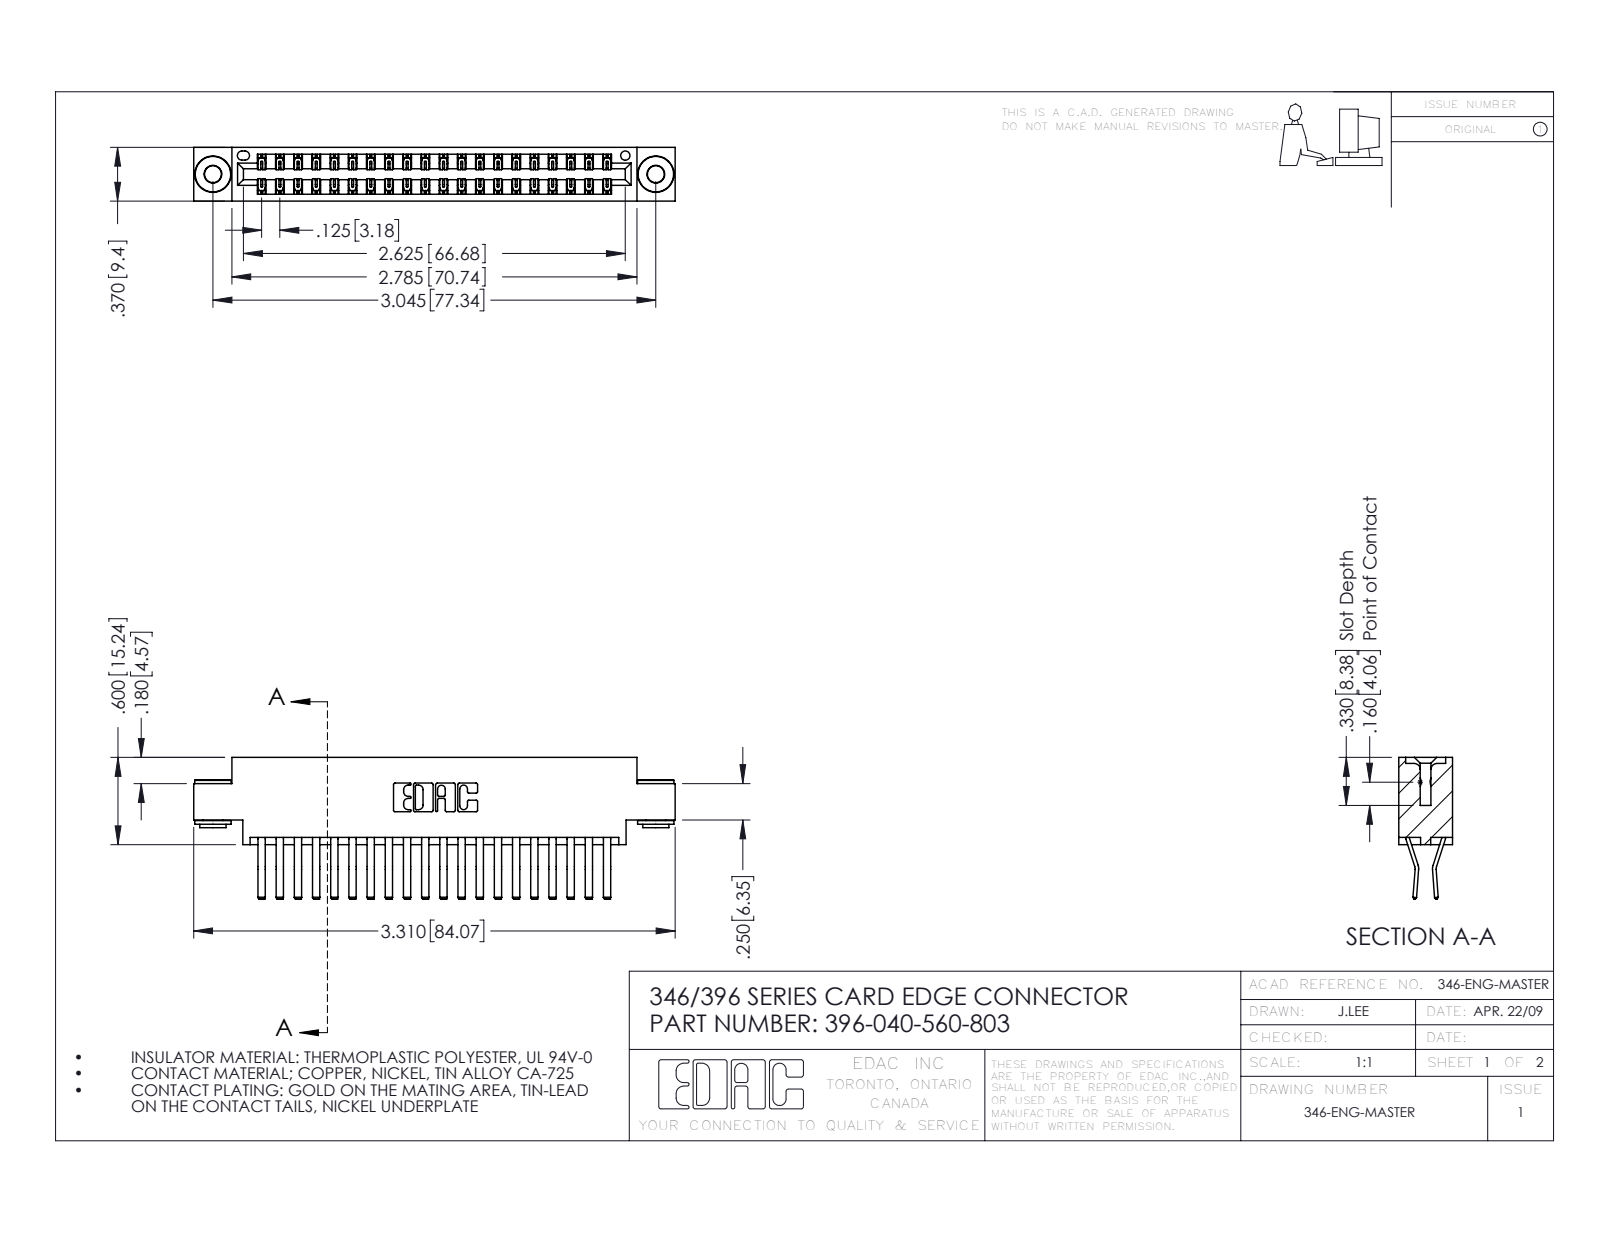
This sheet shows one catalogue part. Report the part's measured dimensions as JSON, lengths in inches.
{"part_name": "346 Part_0.170 Offset - 0.156 Dia-TH; 345-292-001_560 Tail; 396-040-560-803; 345-250-002_345-250-002-102", "step_written_by": "SolidWorks 2016 (CONFIG_CONTROL_DESIGN)", "units": "inches", "bodies": {"solids": 43, "faces": 2324, "planar": 1490, "cylindrical": 826, "other": 8}, "overall_size": [3.31, 0.975, 0.37], "volume_in3": 0.498, "surface_area_in2": 18.53, "round_holes": [[0.116, 2], [0.156, 2], [0.064, 1]], "round_bosses_or_shafts": [[0.25, 2], [0.18, 2], [0.136, 2]], "partial_cylinders_radius": [[0.006, 60], [0.01, 22], [0.007, 6], [0.031, 6], [0.026, 3], [0.01, 2], [0.014, 2], [0.022, 2]], "face_to_face_distances": [0.048, 0.322, 0.37, 0.25, 0.025, 0.275, 0.072, 0.298, 0.148, 0.222], "hole_center_spacings": [0.246, 2.837, 3.045]}
